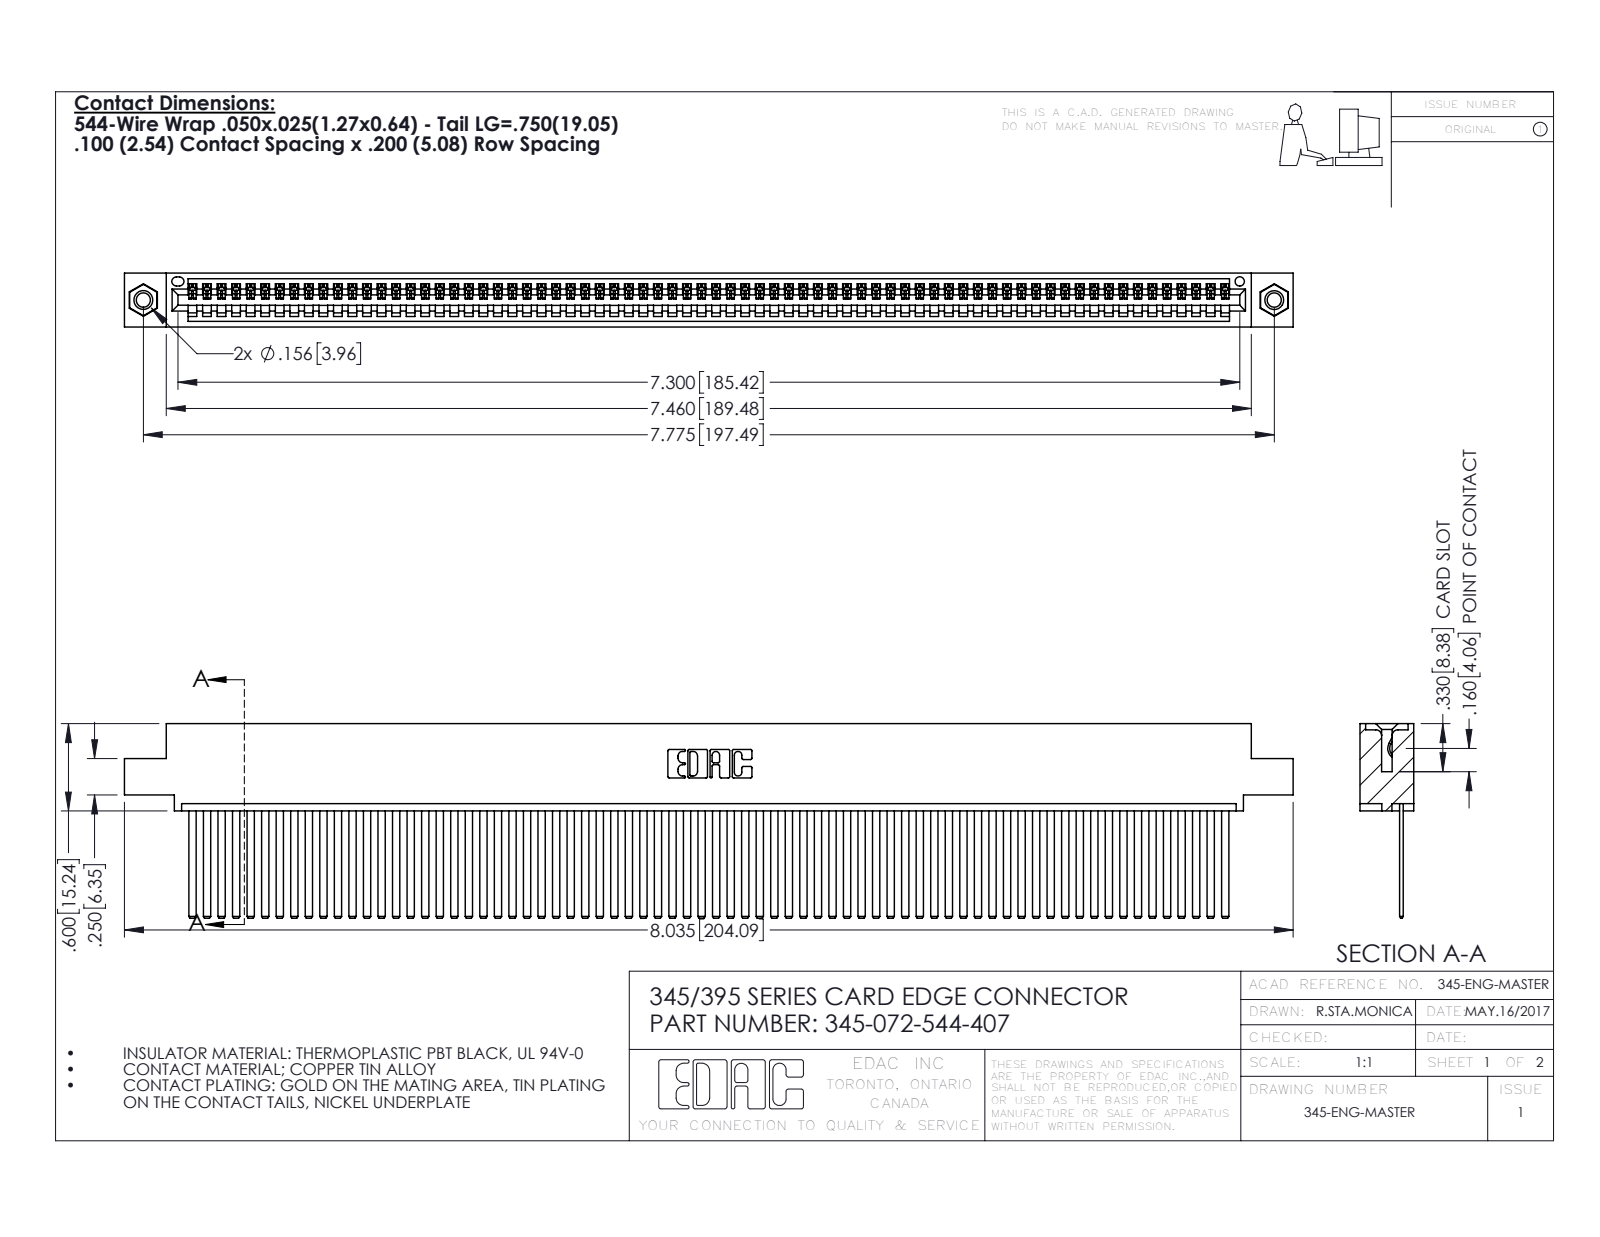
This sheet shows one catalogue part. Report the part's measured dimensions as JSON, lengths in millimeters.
{"part_name": "345-250-001_345-250-005-103; 345 Part_0.110 Offset - 0.156 Dia-TI; 345-072-544-407; 345-292-001_345-293-144", "step_written_by": "SolidWorks 2016 (CONFIG_CONTROL_DESIGN)", "units": "millimeters", "bodies": {"solids": 75, "faces": 3934, "planar": 2708, "cylindrical": 1210, "other": 16}, "overall_size": [204.1, 34, 9.4], "volume_mm3": 20370, "surface_area_mm2": 30100, "round_holes": [[2.5, 2], [3.2, 2], [4, 2], [1.6, 1]], "round_bosses_or_shafts": [[3.9, 2]], "partial_cylinders_radius": [[0.2, 144], [0.3, 22], [0.2, 6], [0.8, 6], [0.7, 3], [0.8, 2], [1, 2], [0.4, 1]], "face_to_face_distances": [1.8, 7.6, 0.6, 2.5, 6.9, 9.4, 5.1, 5.7, 3.8, 1.8], "hole_center_spacings": [6.9, 191.5, 197.5]}
